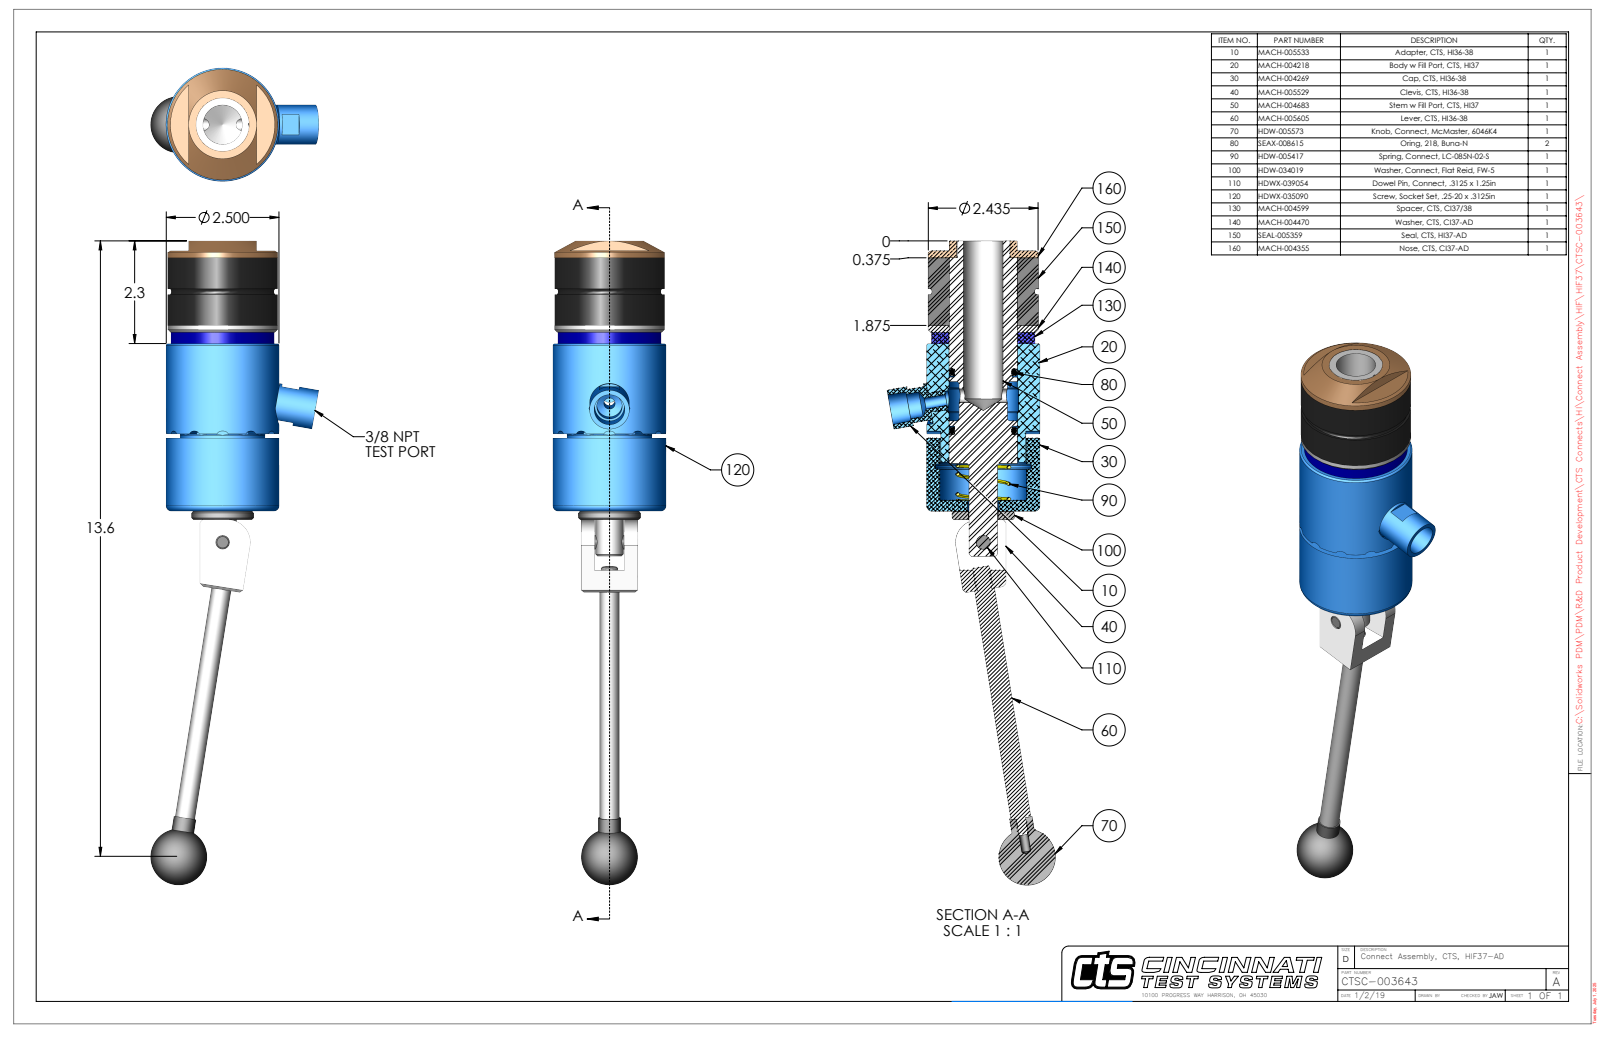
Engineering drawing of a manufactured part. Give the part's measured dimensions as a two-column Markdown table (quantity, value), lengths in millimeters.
| quantity | value |
| --- | --- |
| part name | CTSC-003643 |
| STEP written by | SolidWorks 2023 (AUTOMOTIVE_DESIGN) |
| units | millimeters |
| bodies | 10 solids, 312 faces (110 planar, 129 cylindrical, 73 other) |
| overall size | 362.6 × 94.4 × 63.5 |
| volume | 484 200 mm³ |
| surface area | 98 130 mm² |
| round holes (diameter × count) | 5.1 × 2, 3.8 × 1, 6.4 × 1, 7.9 × 1, 7.9 × 1, 8 × 1, 8 × 1, 14.3 × 1, 16.7 × 1, 17.7 × 1, 22.2 × 1, 29.8 × 1 |
| round bosses / shafts (diameter × count) | 63.5 × 1, 61.8 × 1, 61.8 × 1, 57.9 × 1, 47.6 × 1, 38.1 × 1, 38 × 1, 35.1 × 1 |
| partial cylindrical surfaces (radius × count) | 3 × 12, 0.7 × 2, 4.8 × 1, 5 × 1, 11.9 × 1, 12 × 1, 12.7 × 1, 30 × 1 |
| main face-to-face distances | 38.1, 10.2, 48.3, 6.4, 3.9, 42, 94.3, 100.7, 104.5, 142.6 |
| hole center spacings | 18.8, 53.8, 72.6 |
